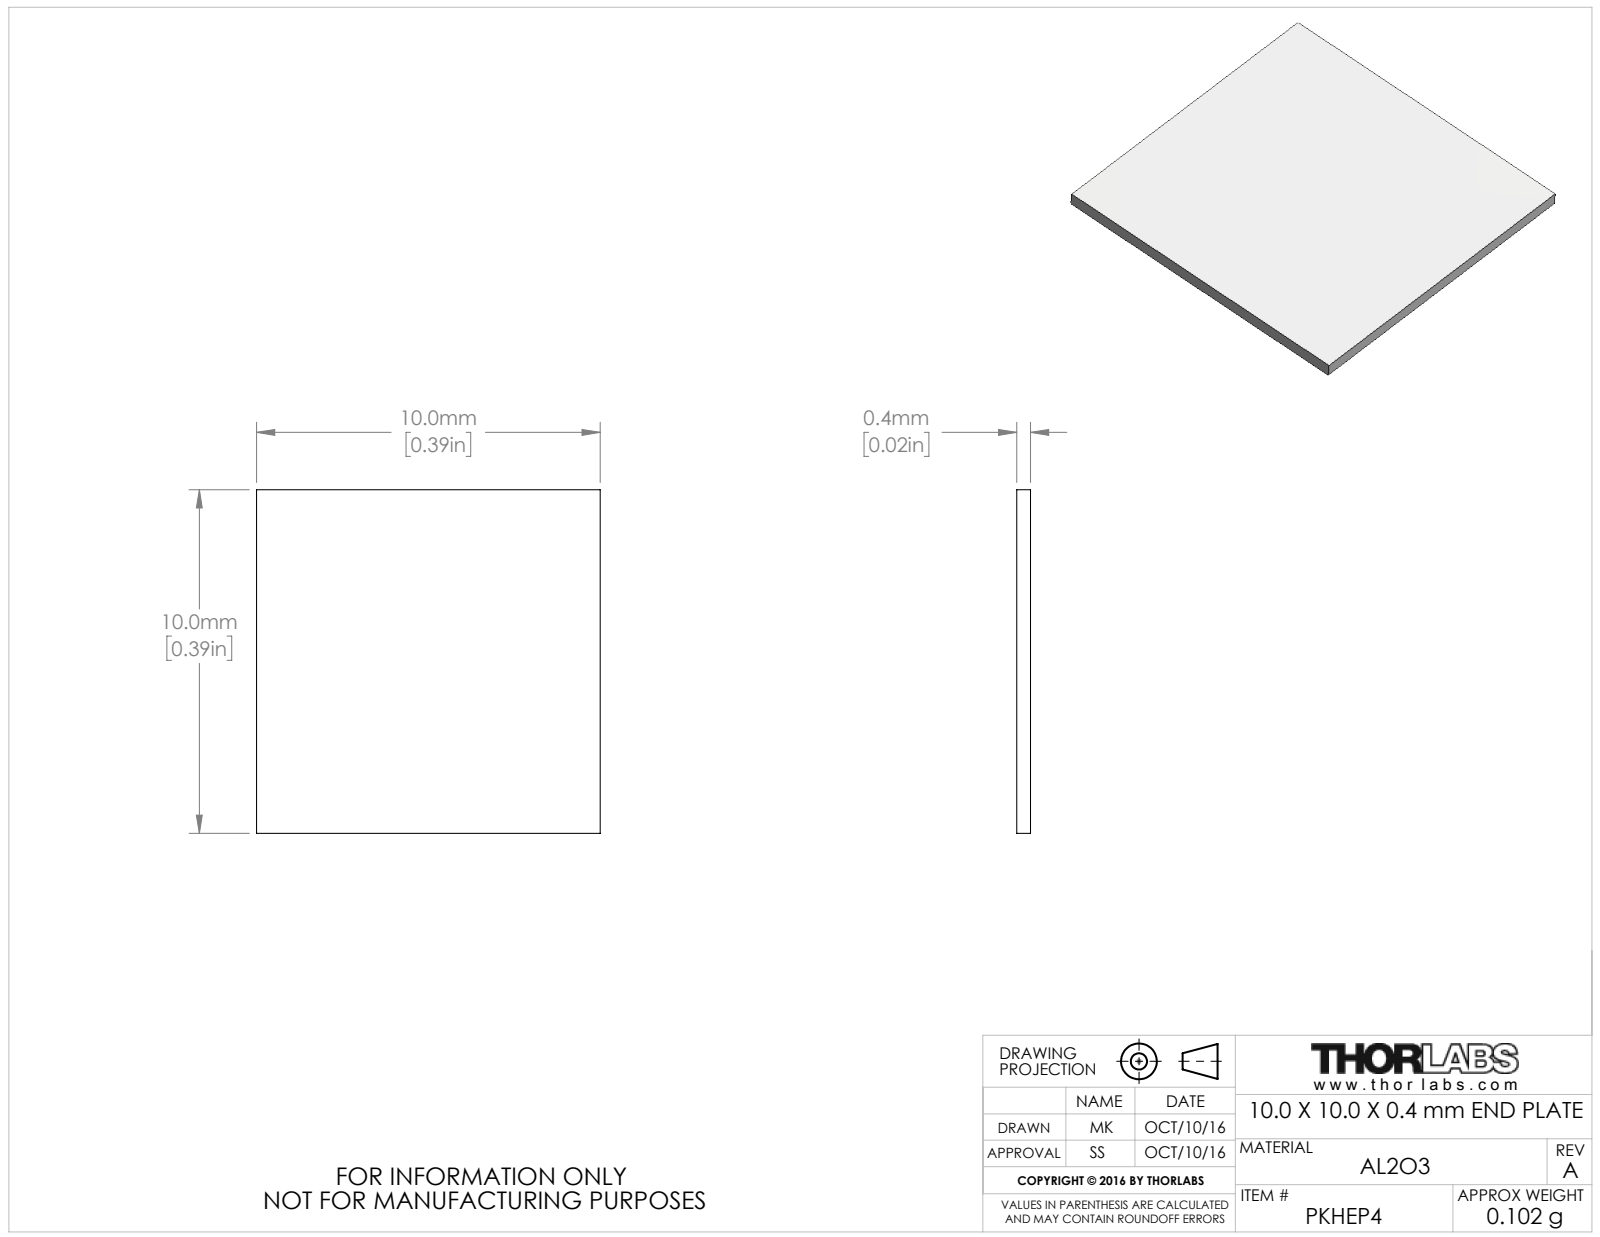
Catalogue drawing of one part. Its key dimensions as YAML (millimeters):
part_name: "CTN002724"
step_written_by: "SolidWorks 2016 (AUTOMOTIVE_DESIGN)"
units: millimeters
bodies: {solids: 1, faces: 6, planar: 6, cylindrical: 0, other: 0}
overall_size: [10, 10, 0.4]
volume: 40
surface_area: 216
face_to_face_distances: [0.4, 10]
